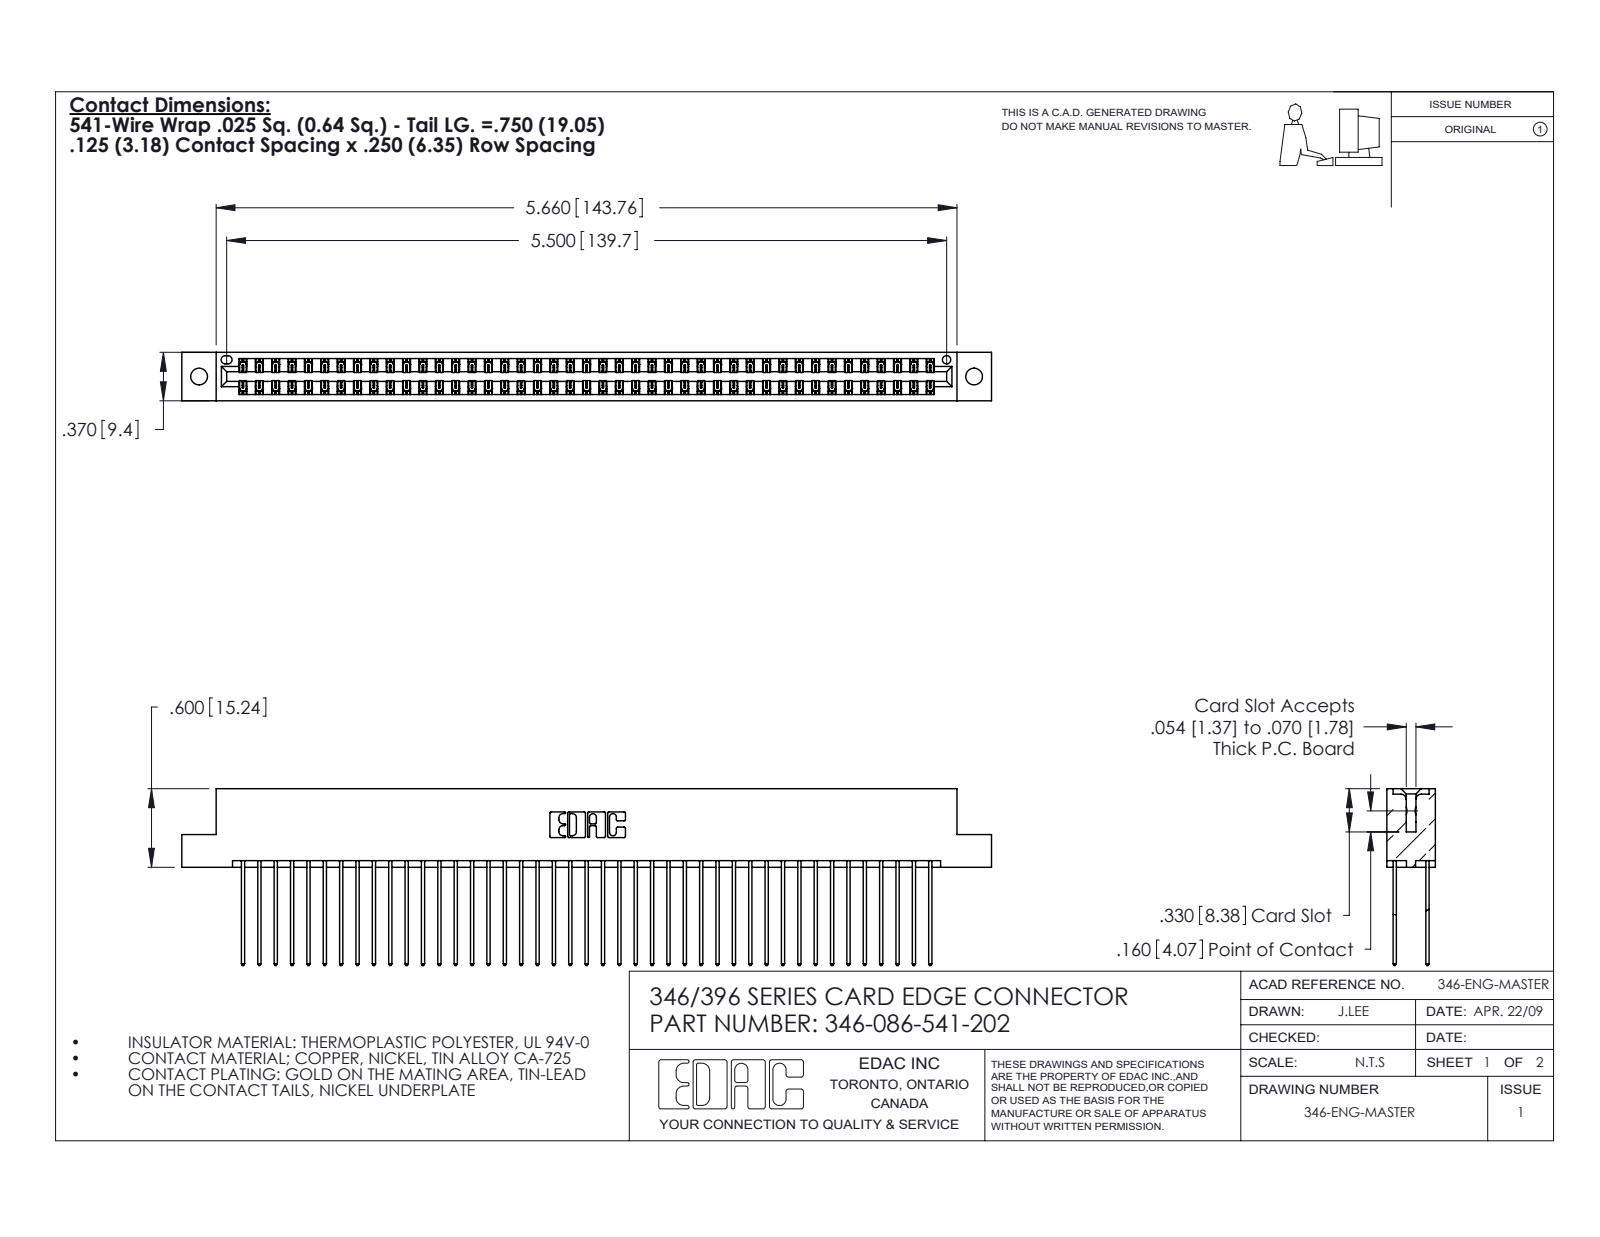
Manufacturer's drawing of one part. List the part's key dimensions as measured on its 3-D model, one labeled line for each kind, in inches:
Part name (STEP PRODUCT): 345-292-001_345-293-141; 346 Part_Flush Mounting Lugs - 0.128 Dia; 346-086-541-202
STEP written by: SolidWorks 2020 (CONFIG_CONTROL_DESIGN)
Units: inches
Bodies: 87 solids, 4594 faces (3086 planar, 1508 cylindrical, 0 other)
Overall size (bounding box): 6.185 × 1.35 × 0.37
Volume: 0.963 in³ · Surface area: 36.9 in²
Round holes (diameter × count): ⌀0.128 ×2, ⌀0.064 ×1
Partial cylindrical surfaces — rounded edges, fillets, slot ends (radius × count): R0.006 ×129, R0.01 ×86, R0.01 ×22, R0.007 ×6, R0.031 ×6, R0.026 ×3, R0.014 ×2, R0.022 ×2
Main face-to-face distances: 0.048, 0.322, 0.25, 0.072, 0.298, 0.025, 0.37, 0.275, 0.225, 0.148
Hole centre spacings: 0.246, 5.711, 5.92
